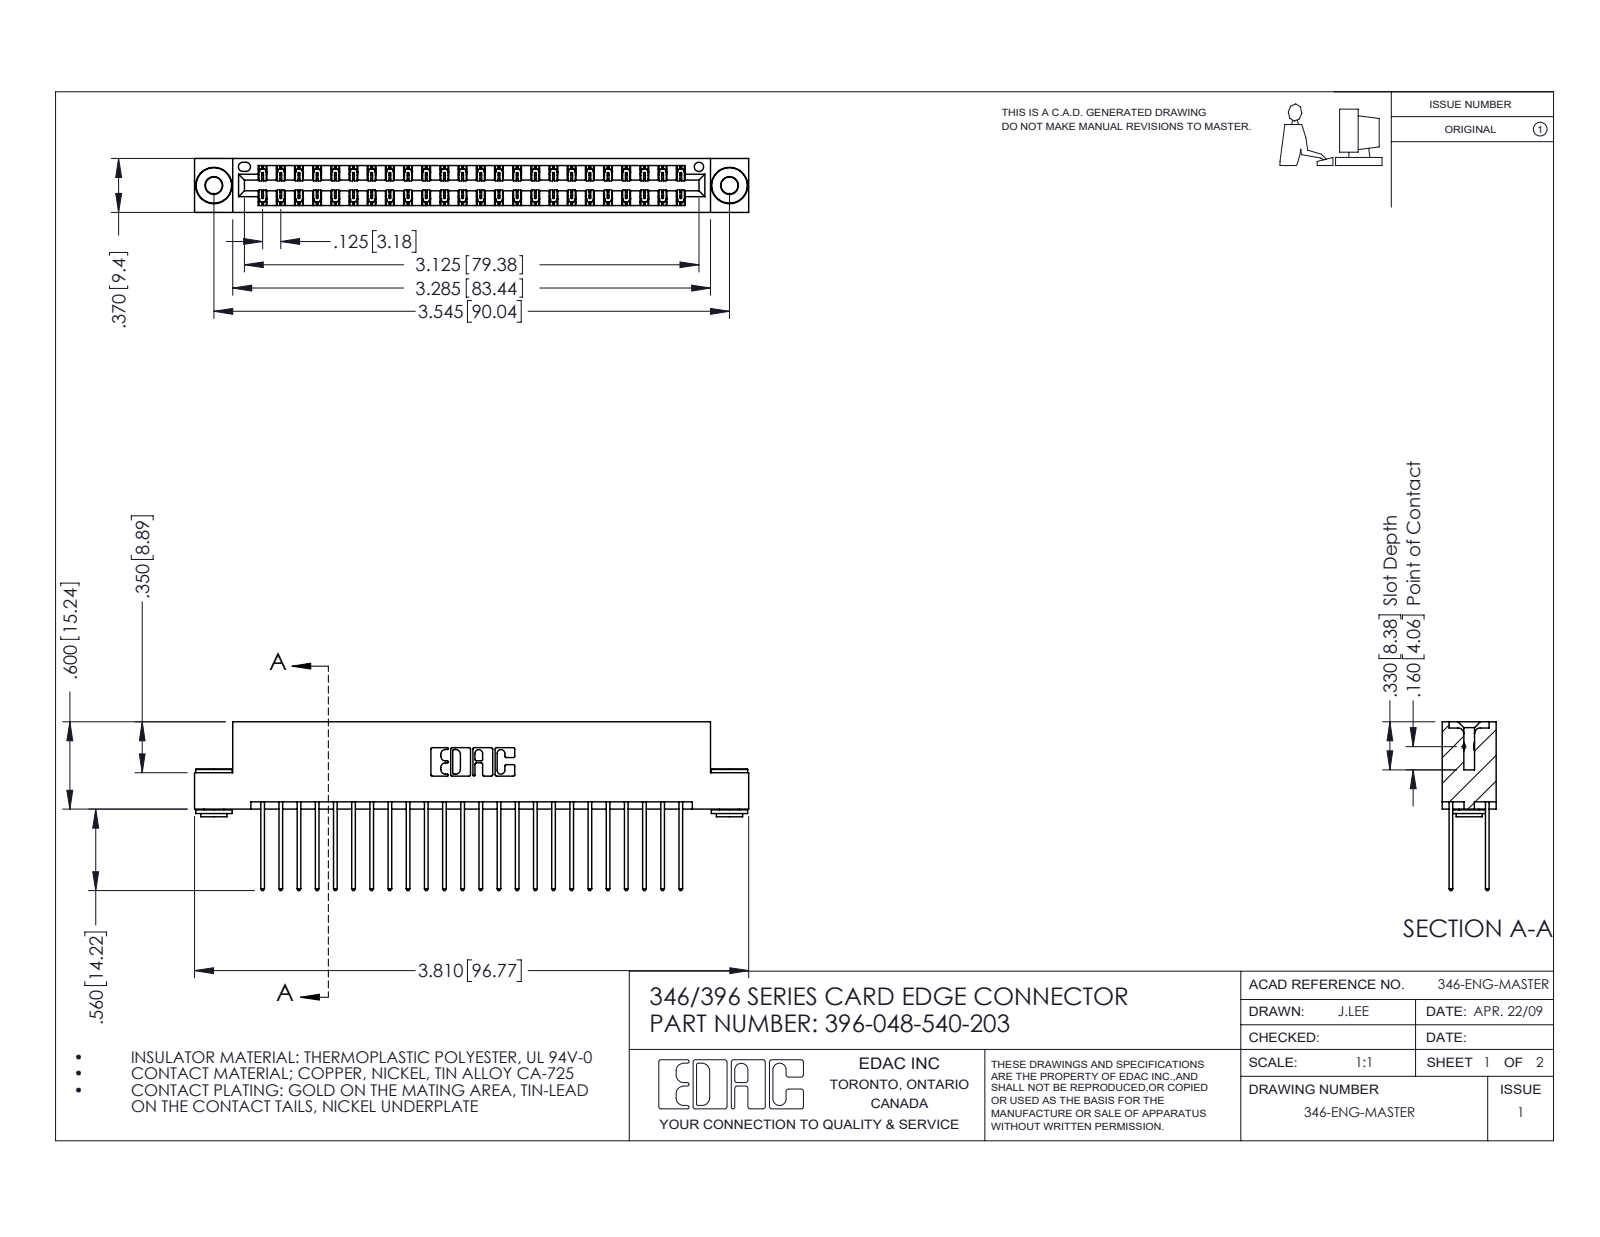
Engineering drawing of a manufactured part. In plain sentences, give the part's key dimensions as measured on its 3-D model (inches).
The part is named "345-292-001_345-293-140; 346 Part_Flush Mounting Lugs - 0.156 Dia-TH; 396-048-540-203; 345-250-002_345-250-002-102". Its 3-D file was written by "SolidWorks 2016 (CONFIG_CONTROL_DESIGN)". It is 51 solids with 2656 faces: 1766 planar, 882 cylindrical and 8 other. Overall it measures 3.81 by 1.16 by 0.37 inches. Its volume is 0.58 cubic inches and its surface area 21.46 square inches. Round holes: 2 of diameter 0.116, 2 of diameter 0.156, 1 of diameter 0.064. Round bosses or shafts: 2 of diameter 0.25, 2 of diameter 0.18, 2 of diameter 0.136. Partial cylindrical surfaces (rounded edges, fillets, slot ends): 72 of radius 0.006, 48 of radius 0.01, 22 of radius 0.01, 6 of radius 0.007, 6 of radius 0.031, 3 of radius 0.026, 2 of radius 0.014, 2 of radius 0.022. The main face-to-face distances are 0.048, 0.322, 0.25, 0.025, 0.072, 0.298, 0.37, 0.275, 0.148, 0.222. The hole center spacings are 0.246, 3.337, 3.545.
